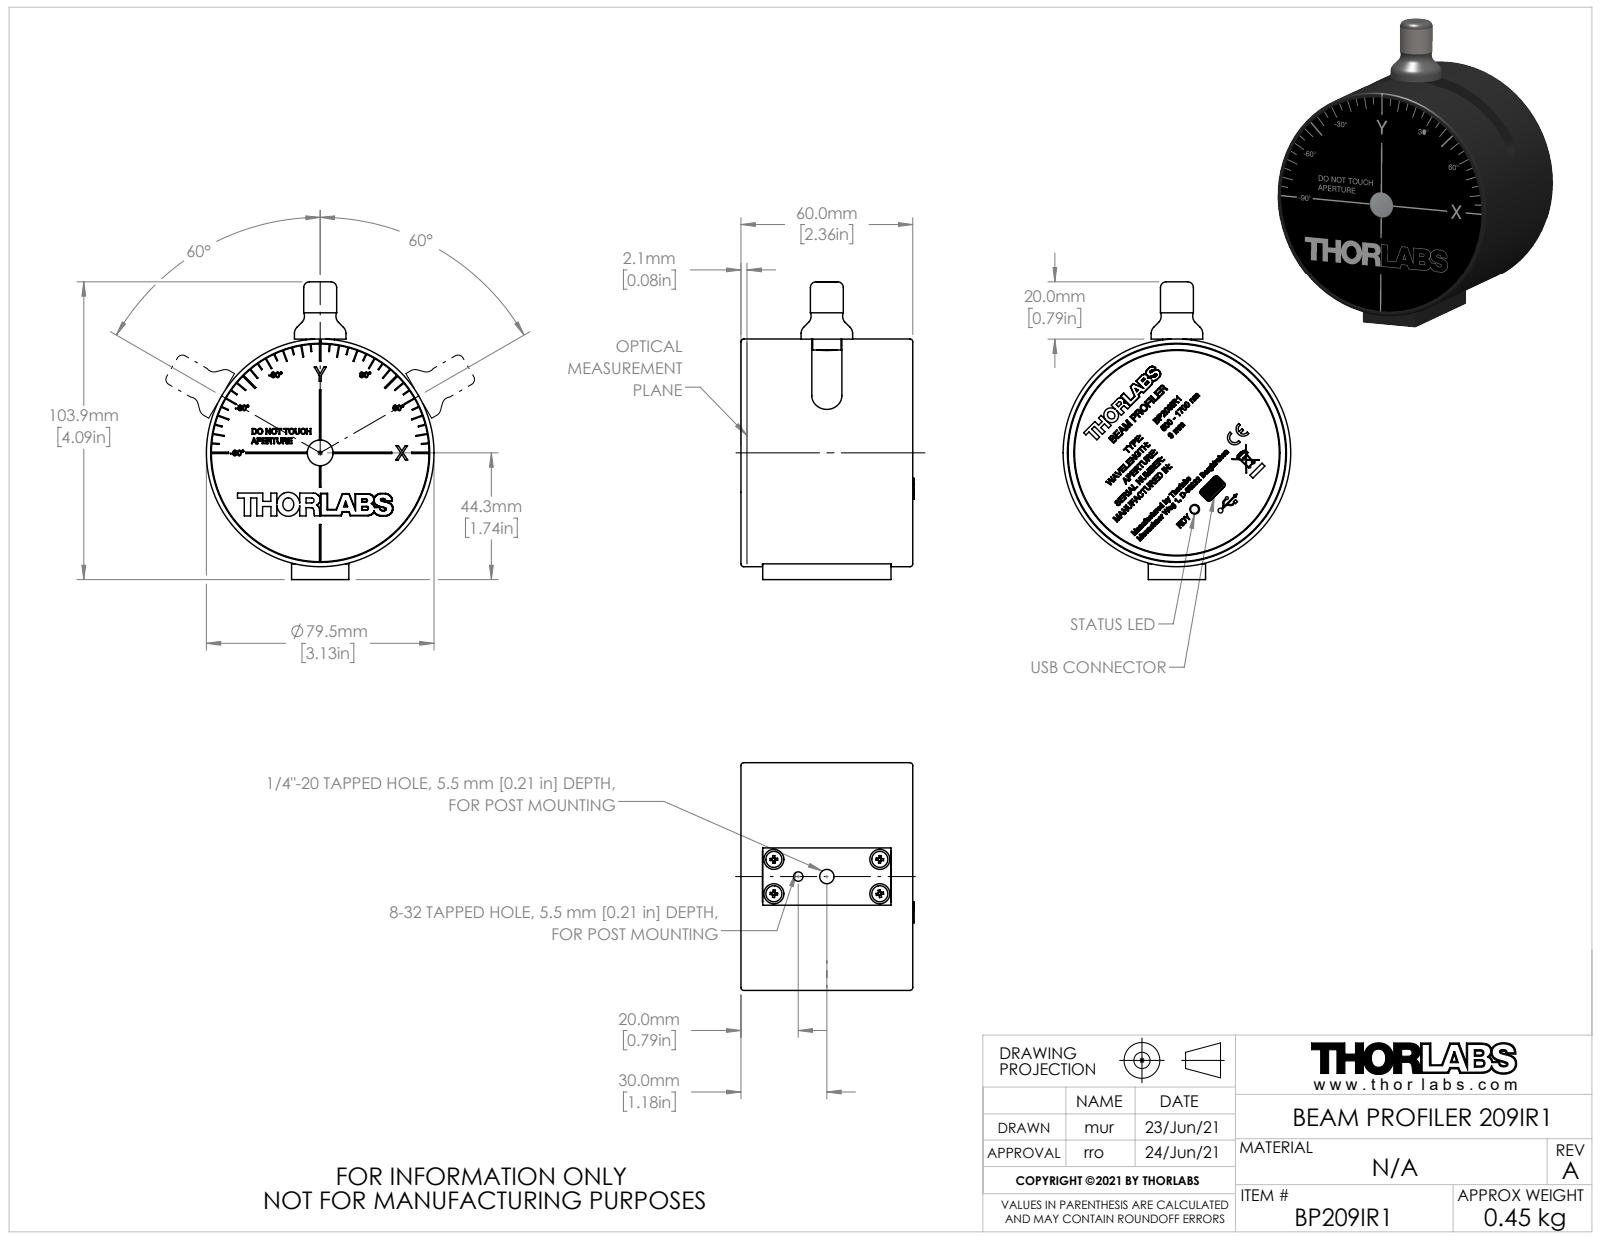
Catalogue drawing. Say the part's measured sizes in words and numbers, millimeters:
The part is named "22.01.17_BP209IR1 WEB". Its 3-D file was written by "SolidWorks 2019 (AUTOMOTIVE_DESIGN)". It is 0 solids with 676 faces: 526 planar, 82 cylindrical and 68 other. Overall it measures 103.95 by 79.5 by 60.5 millimeters. Round holes: 4 of diameter 7, 1 of diameter 2.8, 1 of diameter 3.3, 1 of diameter 3.4, 1 of diameter 5, 1 of diameter 9, 1 of diameter 67, 1 of diameter 72, 1 of diameter 73, 1 of diameter 76.5. Round bosses or shafts: 1 of diameter 79.5, 1 of diameter 76, 1 of diameter 71.8, 1 of diameter 71.5, 1 of diameter 18, 1 of diameter 11.5, 1 of diameter 9.9. Partial cylindrical surfaces (rounded edges, fillets, slot ends): 8 of radius 0.3, 8 of radius 0.7, 7 of radius 1, 2 of radius 5, 2 of radius 5.25, 1 of radius 0.22, 1 of radius 0.55, 1 of radius 0.65. The main face-to-face distances are 60, 59.7, 48.5, 11.2, 11.5, 24.75, 35.25, 48.49, 59.69, 59.99. The hole center spacings are 19.45, 10.4, 12, 29.12, 37, 38.9, 10, 20.65.
